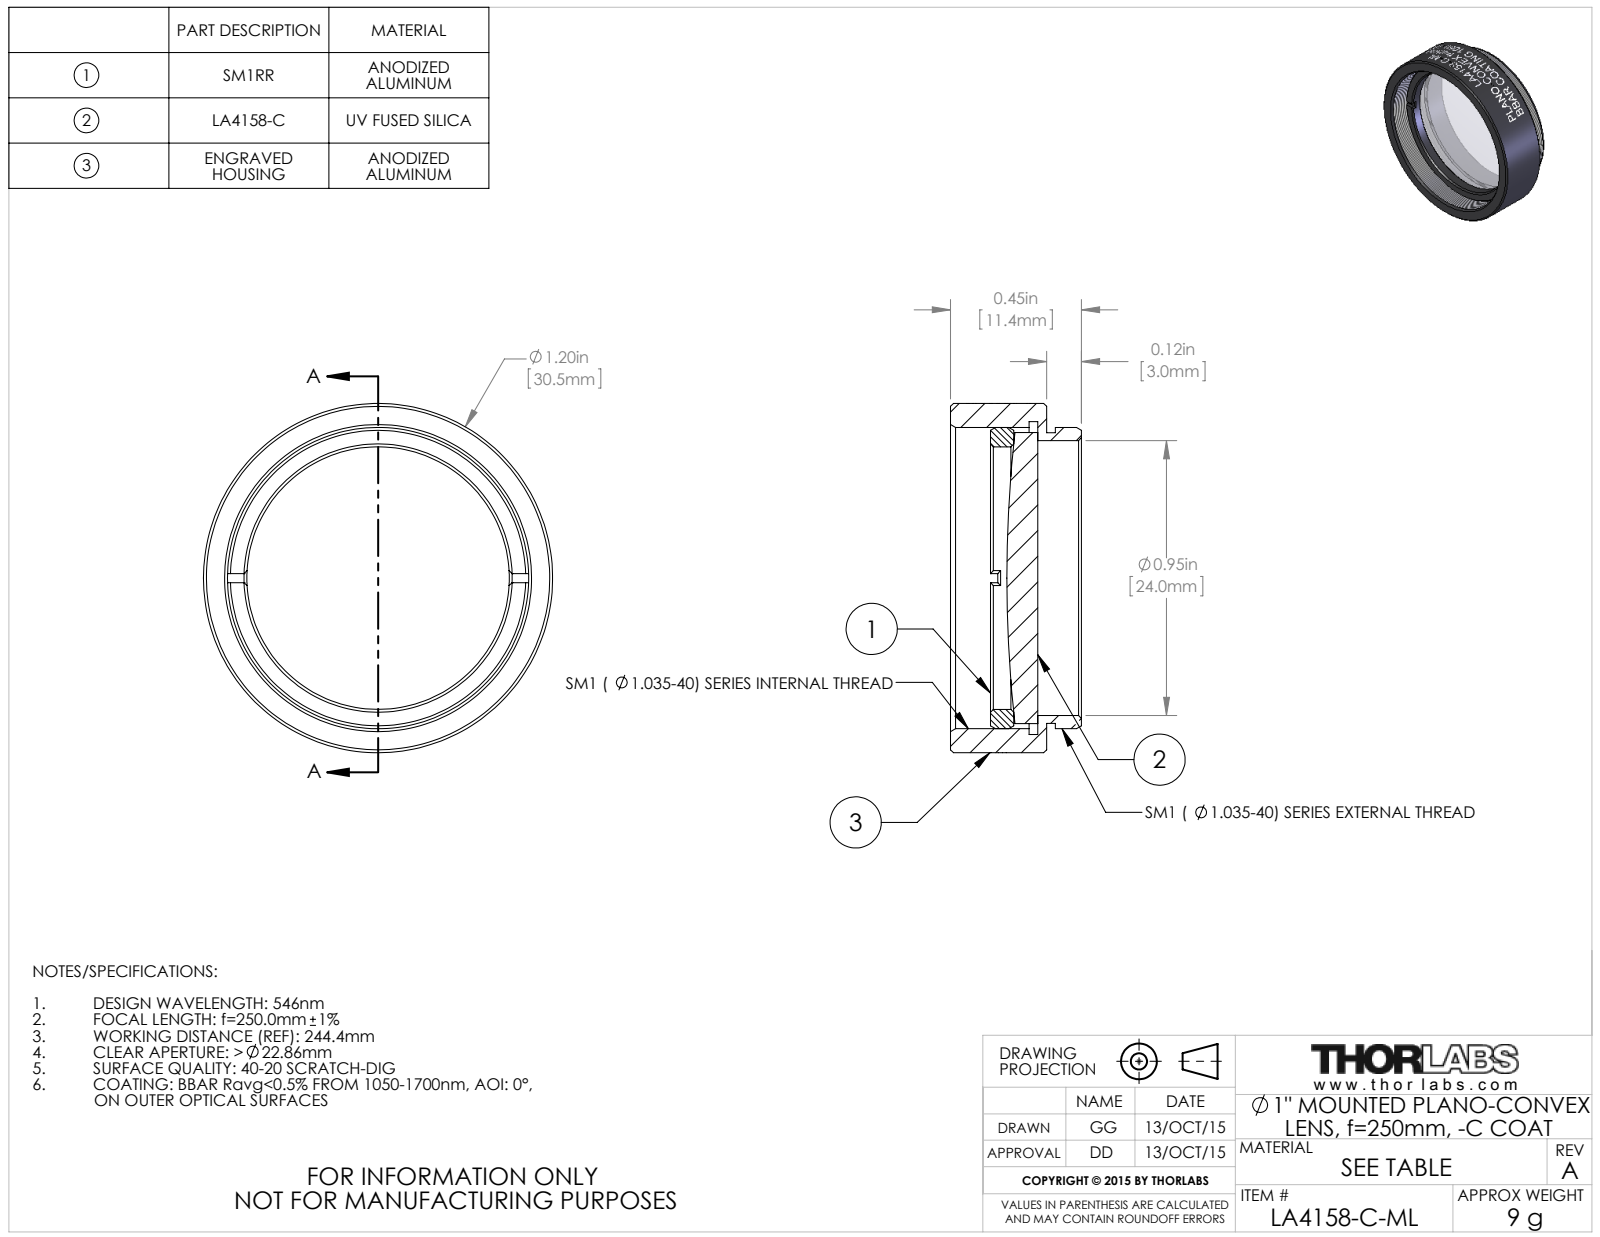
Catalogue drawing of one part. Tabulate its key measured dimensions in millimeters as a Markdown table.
| quantity | value |
| --- | --- |
| part name | TTN039186-E0W |
| STEP written by | SolidWorks 2014 (CONFIG_CONTROL_DESIGN) |
| units | millimeters |
| bodies | 3 solids, 159 faces (20 planar, 115 cylindrical, 24 other) |
| overall size | 30.48 × 30.48 × 11.43 |
| volume | 3 272 mm³ |
| surface area | 4 314 mm² |
| round holes (diameter × count) | 22.91 × 1, 24 × 1, 27.31 × 1 |
| round bosses / shafts (diameter × count) | 30.48 × 1, 26.29 × 1, 25.4 × 1, 25.37 × 1 |
| main face-to-face distances | 0.76, 8.38, 7.62, 2.87, 2.11, 5.51, 4.9, 4.14, 2.03, 3.48 |
